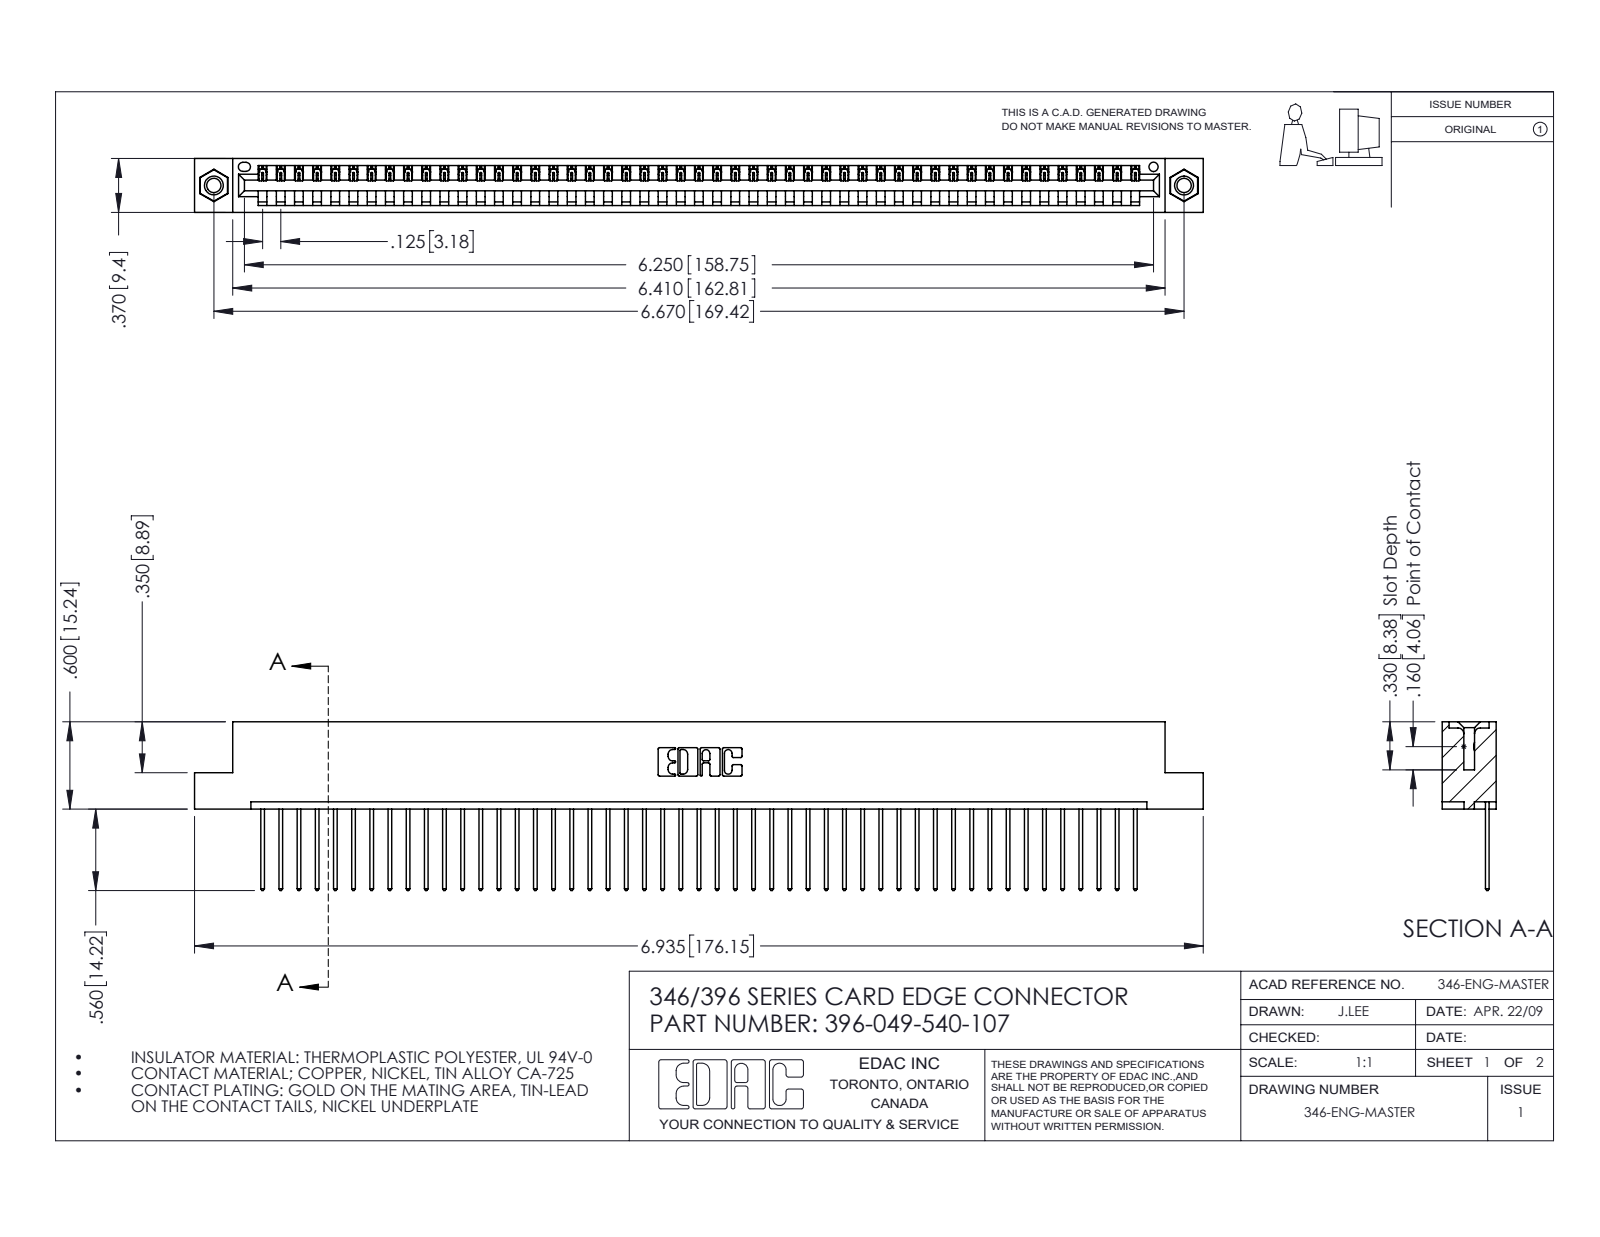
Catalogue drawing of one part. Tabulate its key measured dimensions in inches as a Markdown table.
| quantity | value |
| --- | --- |
| part name | 396-049-540-107; 345-250-001_345-250-005-103; 345-292-001_345-293-140; 346 Part_Flush Mounting Lugs - 0.156 Dia-TI |
| STEP written by | SolidWorks 2016 (CONFIG_CONTROL_DESIGN) |
| units | inches |
| bodies | 52 solids, 3024 faces (2068 planar, 940 cylindrical, 16 other) |
| overall size | 6.935 × 1.16 × 0.37 |
| volume | 1.035 in³ |
| surface area | 33.78 in² |
| round holes (diameter × count) | 0.098 × 2, 0.125 × 2, 0.156 × 2, 0.064 × 1 |
| round bosses / shafts (diameter × count) | 0.155 × 2 |
| partial cylindrical surfaces (radius × count) | 0.006 × 98, 0.01 × 98, 0.01 × 22, 0.007 × 6, 0.031 × 6, 0.026 × 3, 0.031 × 2, 0.04 × 2 |
| main face-to-face distances | 0.048, 0.322, 0.37, 0.25, 0.072, 0.298, 0.025, 0.148, 0.222, 0.1 |
| hole center spacings | 0.246, 6.461, 6.67 |
